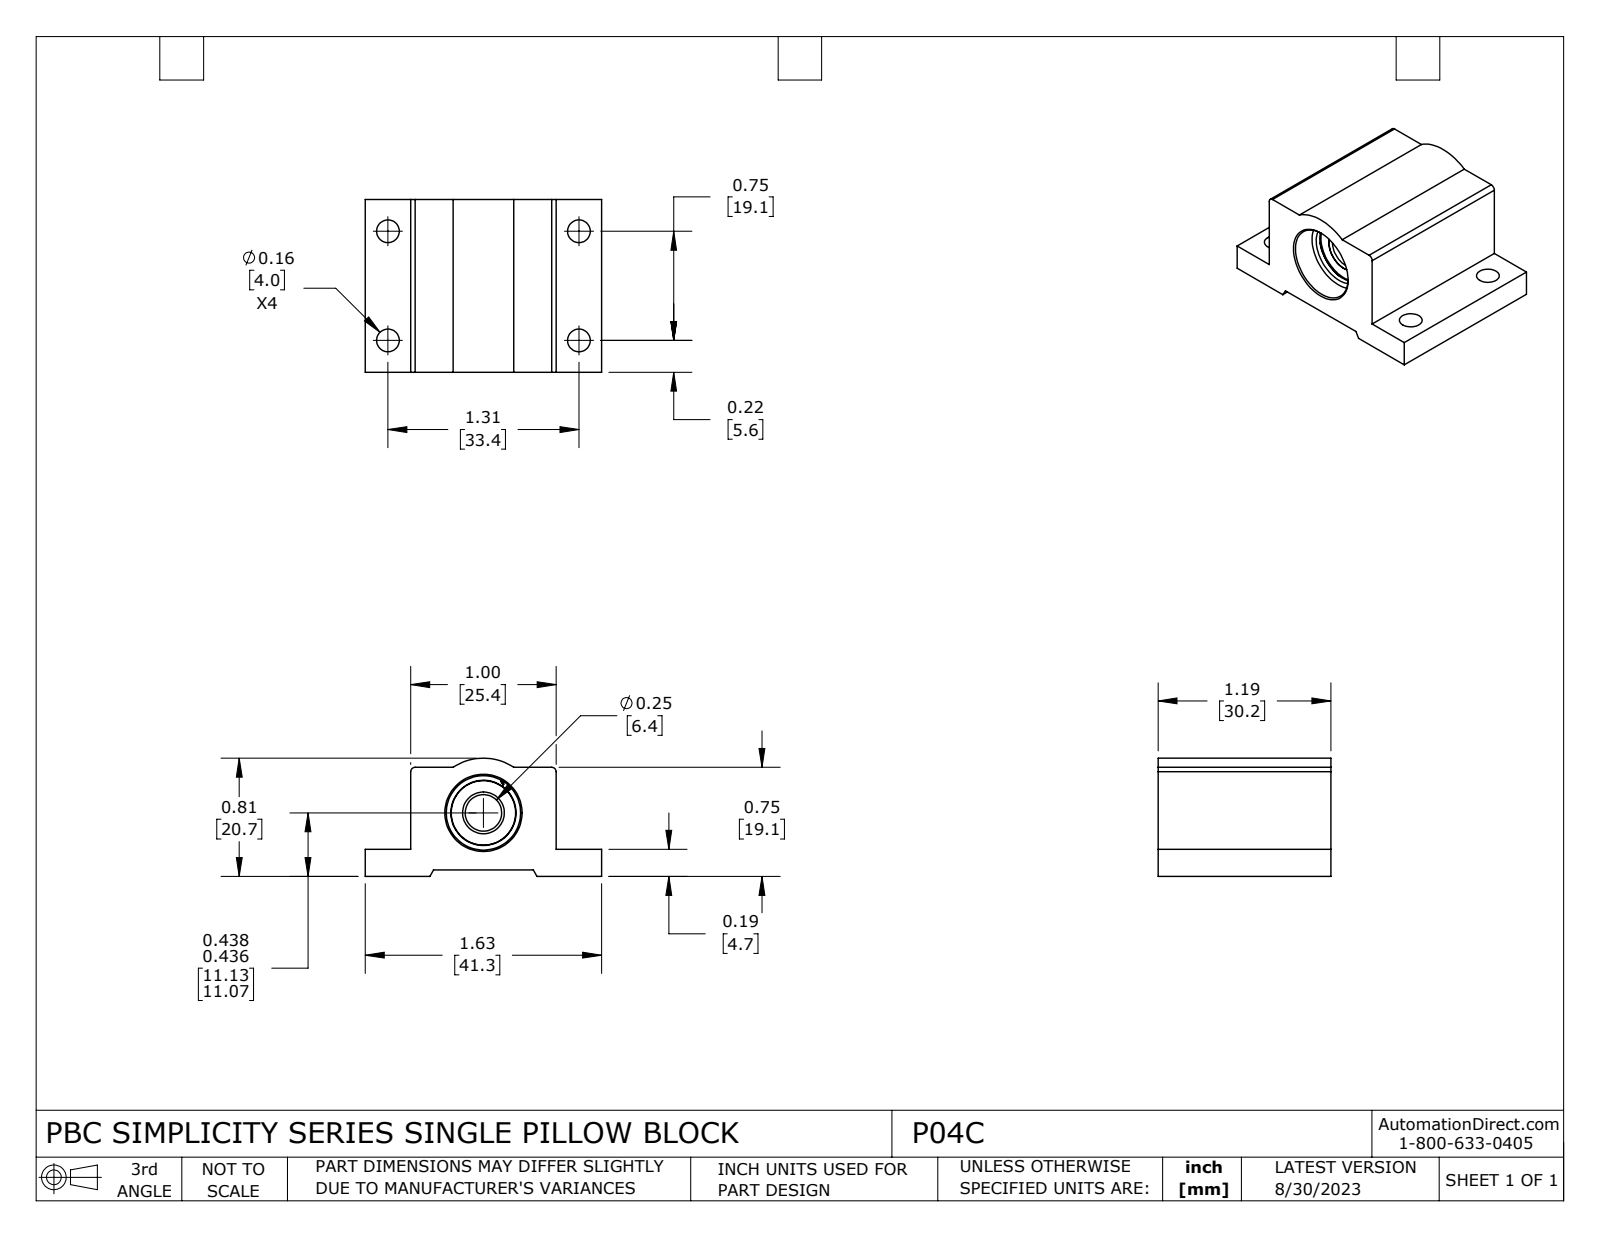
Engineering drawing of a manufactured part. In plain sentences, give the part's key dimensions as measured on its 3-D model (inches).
The part is named "P04C". Its 3-D file was written by "SolidWorks 2021 (CONFIG_CONTROL_DESIGN)". It is 7 solids with 164 faces: 45 planar, 71 cylindrical and 48 other. Overall it measures 1.625 by 1.187 by 0.813 inches. Its volume is 0.864 cubic inches and its surface area 13.87 square inches. Round holes: 4 of diameter 0.156, 1 of diameter 0.251, 1 of diameter 0.287, 1 of diameter 0.448, 1 of diameter 0.511, 1 of diameter 0.532. Round bosses or shafts: 1 of diameter 0.538, 1 of diameter 0.499, 1 of diameter 0.467, 1 of diameter 0.399. Partial cylindrical surfaces (rounded edges, fillets, slot ends): 4 of radius 0.008, 2 of radius 0.013, 2 of radius 0.03, 1 of radius 0.376. The main face-to-face distances are 0.045, 0.75, 0.187, 0.142, 1, 1.187, 0.705, 0.563, 0.313, 1.313. The hole center spacings are 0.75, 1.313, 1.513.
